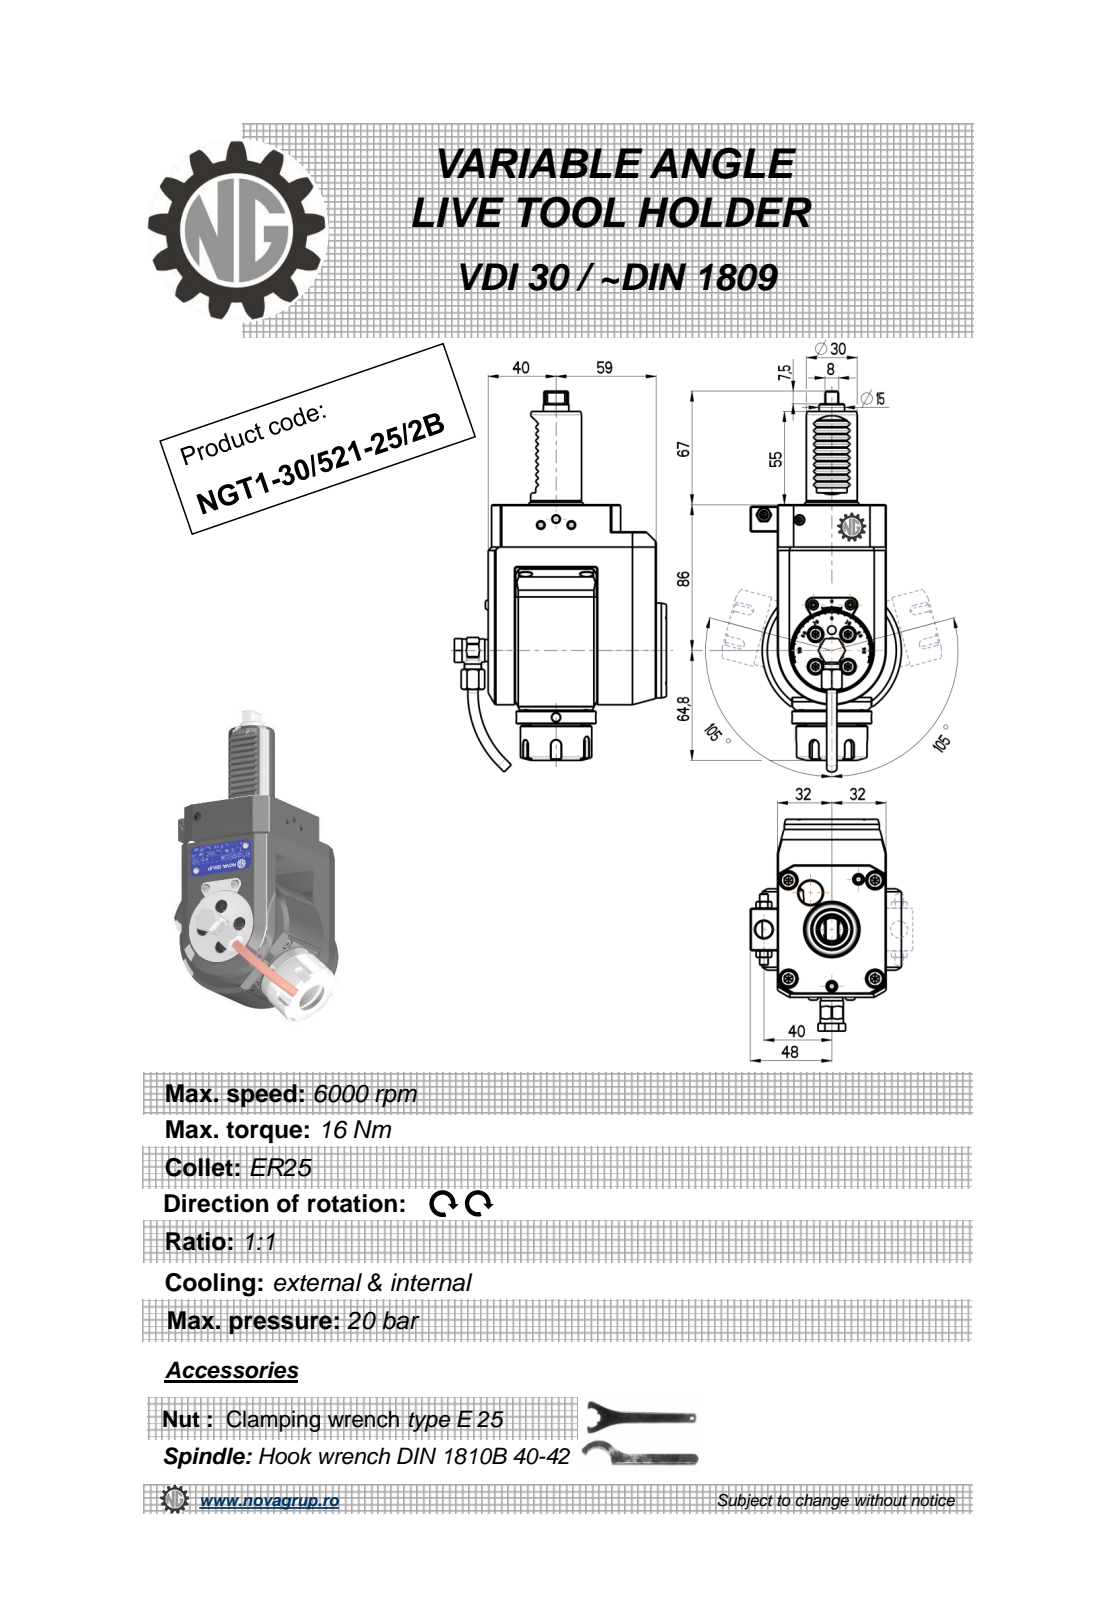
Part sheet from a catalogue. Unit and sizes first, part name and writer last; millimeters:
Units: millimetres
Overall size (bounding box): 224.67 × 124.9 × 89
Round holes (diameter × count): ⌀4 ×5, ⌀3 ×1, ⌀4.2 ×1, ⌀6.2 ×1, ⌀9 ×1, ⌀9.5 ×1, ⌀10 ×1, ⌀11 ×1, ⌀20.3 ×1
Round bosses / shafts (diameter × count): ⌀10 ×2, ⌀6 ×2, ⌀5.7 ×2, ⌀56 ×1, ⌀42 ×1, ⌀40 ×1, ⌀32.99 ×1, ⌀30 ×1
Partial cylindrical surfaces — rounded edges, fillets, slot ends (radius × count): R0.26 ×12, R0.3 ×10, R0.16 ×6, R3 ×5, R0.5 ×4, R0.8 ×2, R1 ×2, R7.2 ×1
Main face-to-face distances: 64, 16, 37, 6, 99, 105, 14, 21, 62, 83
Hole centre spacings: 0.4, 38.95, 40, 49, 49.4, 63.25, 63.56, 89.44
Volume: 798 058 mm³ · Surface area: 74 467 mm²
Bodies: 1 solid, 569 faces (245 planar, 144 cylindrical, 180 other)
Part name (STEP PRODUCT): NGT1_30_521_25_2B
STEP written by: PRO/ENGINEER BY PARAMETRIC TECHNOLOGY CORPORATION, 2010280 (CONFIG_CONTROL_DESIGN)
